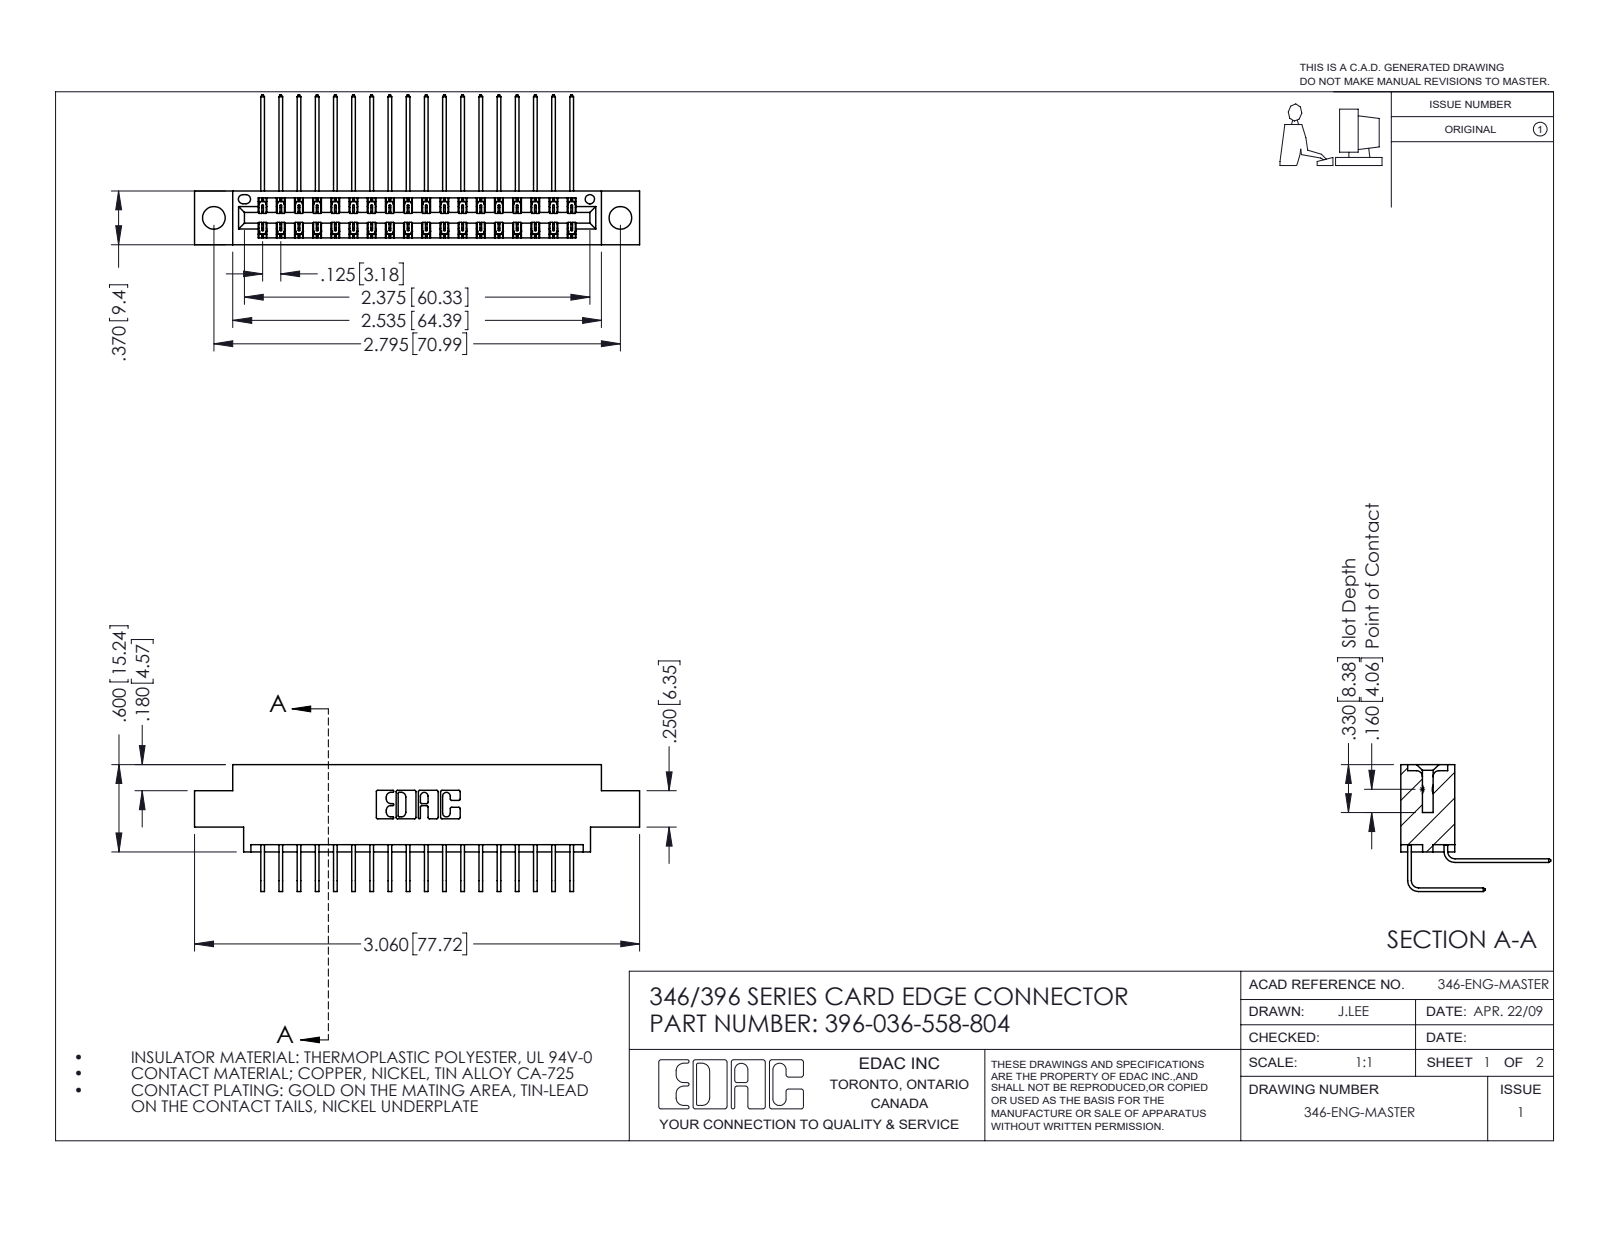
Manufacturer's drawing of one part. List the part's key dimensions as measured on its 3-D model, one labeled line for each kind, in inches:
Part name (STEP PRODUCT): 396-036-558-804; 345-292-001_558 559 Tail - 1; 346 Part_0.170 Offset - 0.156 Dia-TH; 345-292-001_558 Tail - 2
STEP written by: SolidWorks 2016 (CONFIG_CONTROL_DESIGN)
Units: inches
Bodies: 37 solids, 2070 faces (1412 planar, 658 cylindrical, 0 other)
Overall size (bounding box): 3.06 × 1.03 × 0.873
Volume: 0.449 in³ · Surface area: 16.63 in²
Round holes (diameter × count): ⌀0.156 ×2, ⌀0.064 ×1
Partial cylindrical surfaces — rounded edges, fillets, slot ends (radius × count): R0.006 ×54, R0.01 ×22, R0.007 ×6, R0.031 ×6, R0.026 ×3, R0.014 ×2, R0.022 ×2, R0.024 ×2
Main face-to-face distances: 0.322, 0.048, 0.37, 0.25, 0.025, 0.298, 0.072, 0.275, 0.148, 0.222
Hole centre spacings: 0.246, 2.588, 2.795
